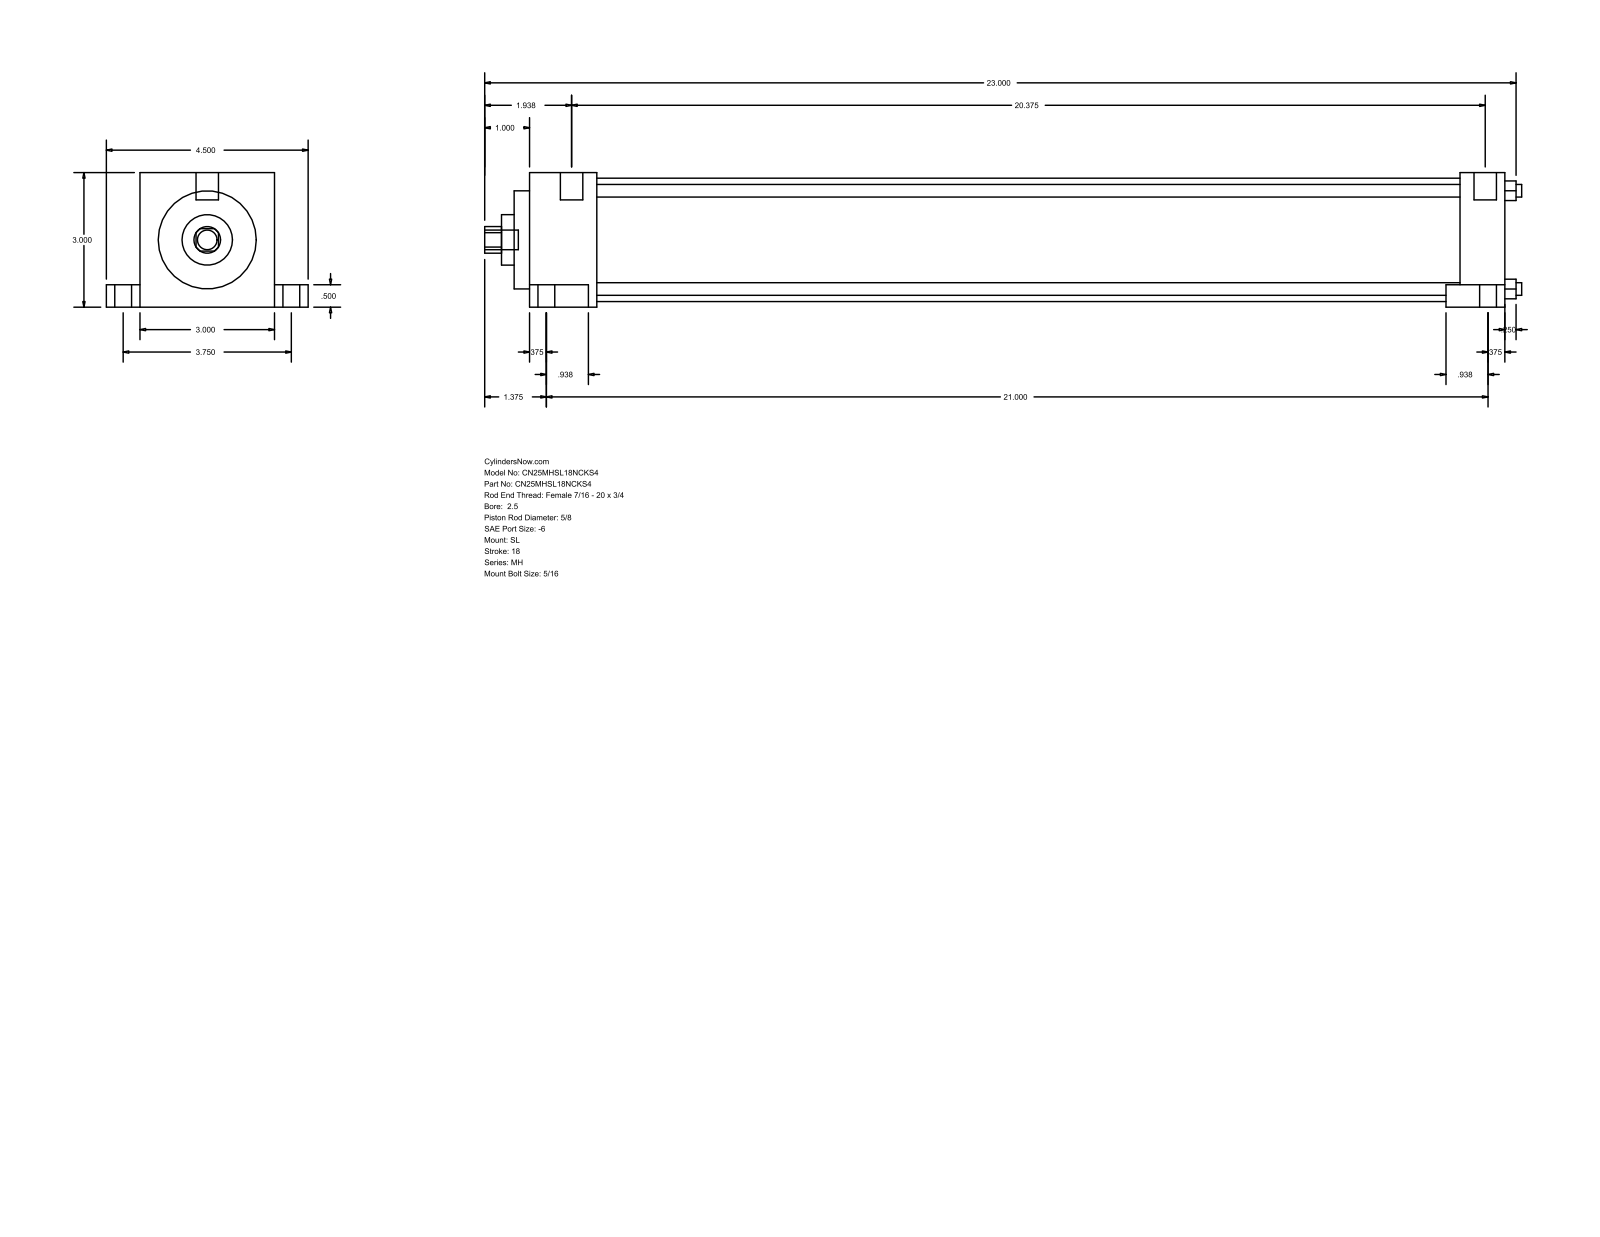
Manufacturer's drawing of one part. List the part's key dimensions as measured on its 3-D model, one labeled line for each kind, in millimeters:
Part name (STEP PRODUCT): MH_SL__0250_0.625
STEP written by: GSSL Pune (CONFIG_CONTROL_DESIGN)
Units: millimetres
Bodies: 0 solids, 86 faces (61 planar, 25 cylindrical, 0 other)
Overall size (bounding box): 587.38 × 114.3 × 76.2
Round holes (diameter × count): ⌀7.14 ×4, ⌀15.88 ×1, ⌀28.57 ×1, ⌀55.55 ×1, ⌀69.85 ×1
Round bosses / shafts (diameter × count): ⌀15.88 ×2, ⌀9.53 ×2, ⌀5.56 ×2, ⌀12.7 ×1, ⌀11.11 ×1
Partial cylindrical surfaces — rounded edges, fillets, slot ends (radius × count): R7.54 ×1
Main face-to-face distances: 76.2, 25.4, 535.78, 561.18, 12.7, 63.5, 19.05, 95.25, 31.75, 527.84
Hole centre spacings: 39.33, 55.62, 78.66
